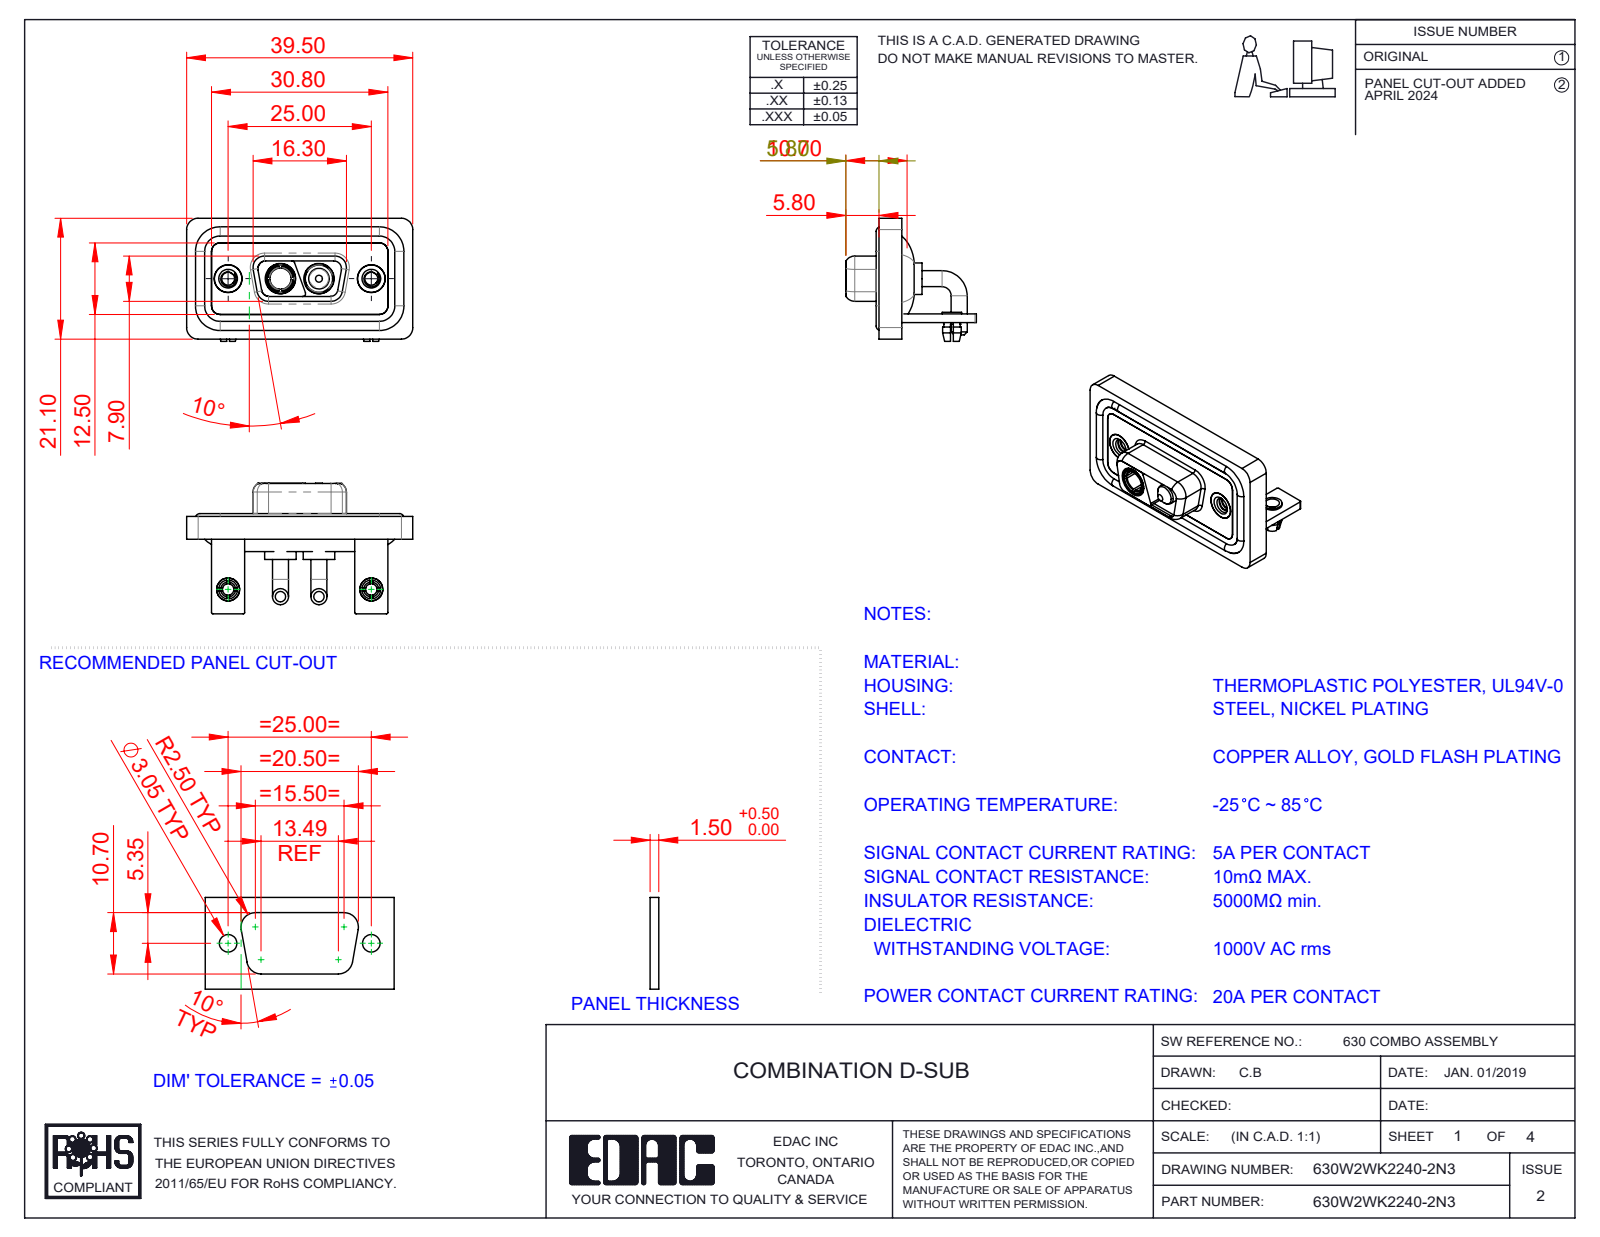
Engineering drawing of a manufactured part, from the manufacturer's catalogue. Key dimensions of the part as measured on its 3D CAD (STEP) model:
Part name (STEP PRODUCT): 630W2WK2140-2N3; 630Combo Shell Rear_09 Contacts; 630Combo Threaded Rivet_2; 630Combo Board Lock_50 Contacts (+6 more)
STEP written by: SolidWorks 2023 (CONFIG_CONTROL_DESIGN)
Units: millimetres
Bodies: 15 solids, 648 faces (212 planar, 291 cylindrical, 145 other)
Overall size (bounding box): 39.5 × 22.8 × 21.5
Volume: 5 109 mm³ · Surface area: 8 440 mm²
Round holes (diameter × count): ⌀4.85 ×4, ⌀2 ×2, ⌀2.26 ×2, ⌀2.5 ×2, ⌀3.2 ×2, ⌀4 ×2, ⌀4.05 ×2, ⌀5 ×2, ⌀5.3 ×2, ⌀3.7 ×1
Round bosses / shafts (diameter × count): ⌀2.8 ×4, ⌀1.6 ×4, ⌀5.5 ×2, ⌀5.2 ×2, ⌀4.95 ×2, ⌀4.8 ×2, ⌀4.75 ×2, ⌀4 ×2
Partial cylindrical surfaces — rounded edges, fillets, slot ends (radius × count): R2 ×19, R1.5 ×18, R0.25 ×16, R1.35 ×8, R1.6 ×8, R0.5 ×7, R0.6 ×4, R0.65 ×4
Main face-to-face distances: 0.4, 2.9, 1.5, 1.1, 3.7, 1.8, 0.8, 2.5, 1.6, 3.1
Hole centre spacings: 9.14, 15.86, 25, 6.72
